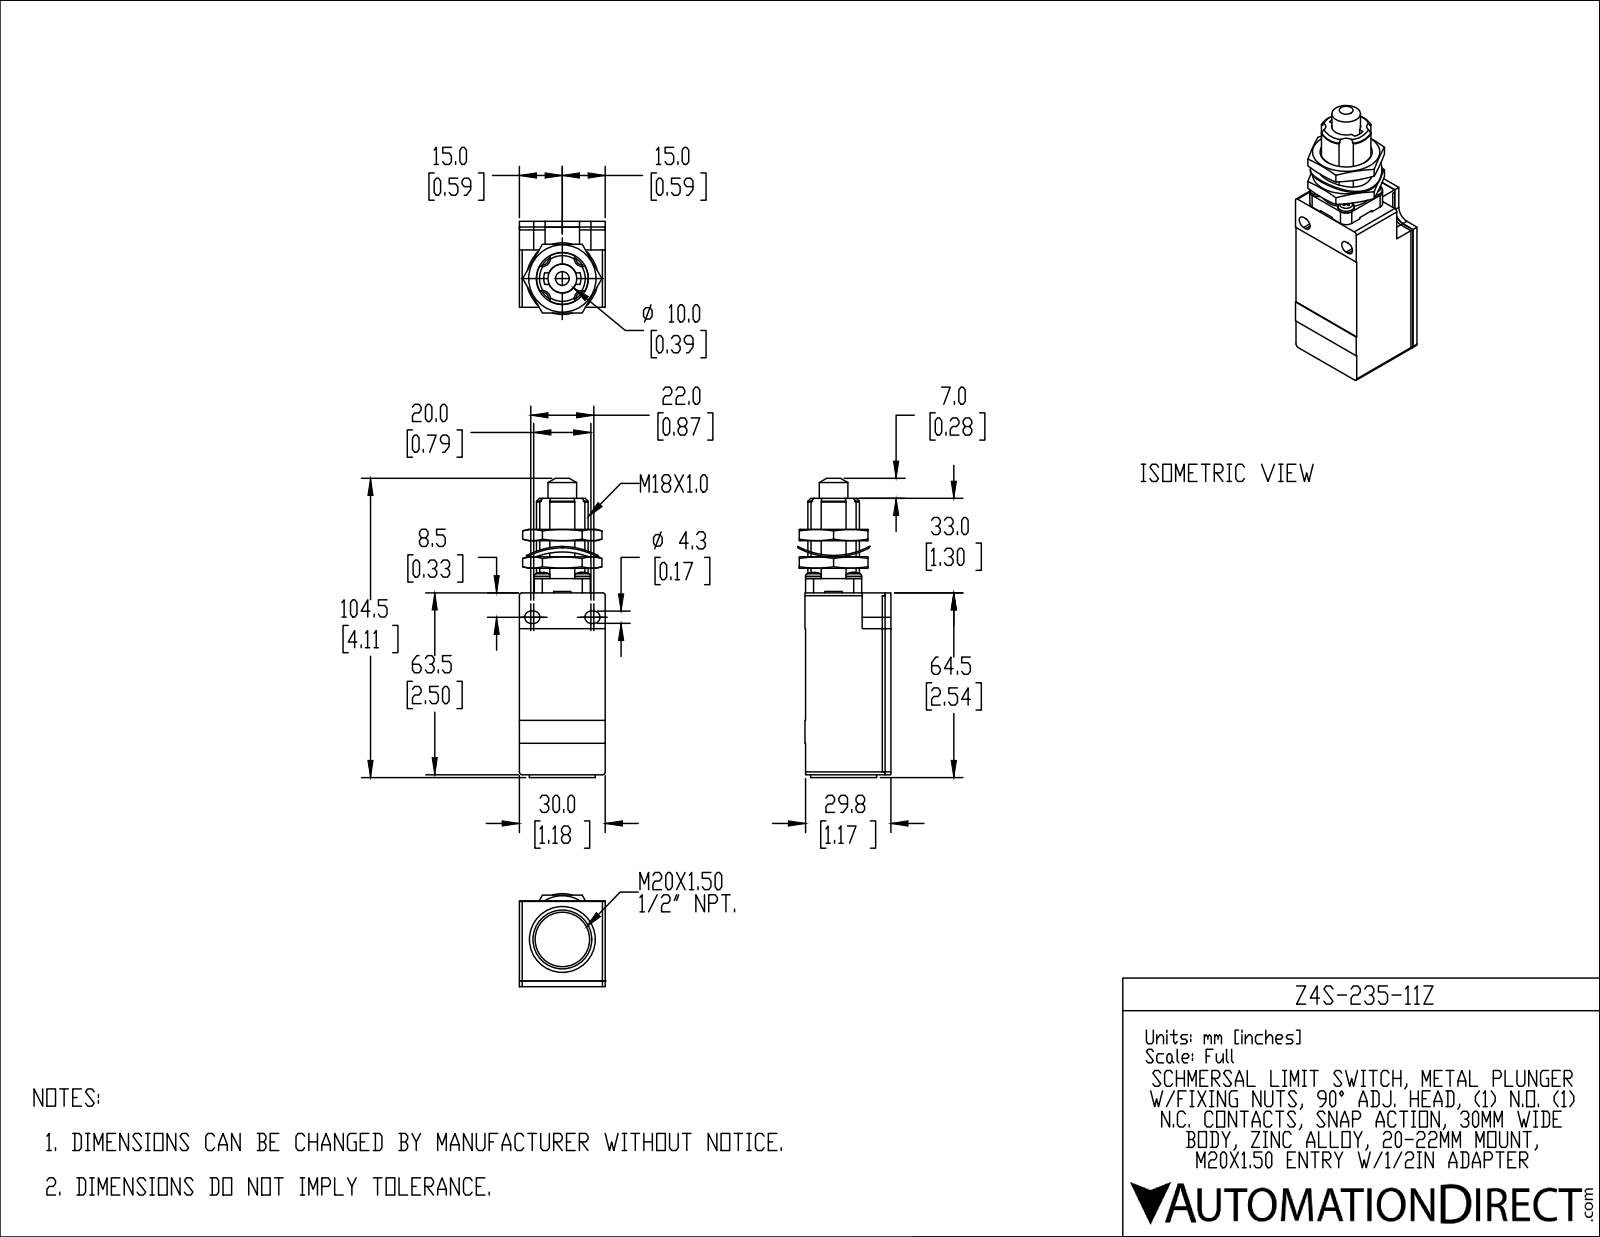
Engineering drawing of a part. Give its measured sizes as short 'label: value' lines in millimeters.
name: Z4S-235-11Z
written by: SolidWorks 2019 (AUTOMOTIVE_DESIGN)
unit: mm
bodies: 2 solids, 367 faces (253 planar, 88 cylindrical, 26 other)
size: 104.5 × 32.5 × 30
volume: 62 520 mm³; area: 16 540 mm²
holes: 3× ⌀7, 1× ⌀13, 1× ⌀13.8, 1× ⌀18.6, 1× ⌀19
bosses: 4× ⌀5.4, 3× ⌀6.5, 1× ⌀25, 1× ⌀23, 1× ⌀10.5, 1× ⌀10
rounds: 12× R0.5, 4× R1, 4× R2.2, 4× R2.8, 4× R2.8, 2× R4, 2× R4, 2× R26.5
face distances: 30, 29.8, 63.5, 4, 2, 9.6, 24, 5.3, 58.2, 9
hole spacings: 56.6, 3.5, 22
